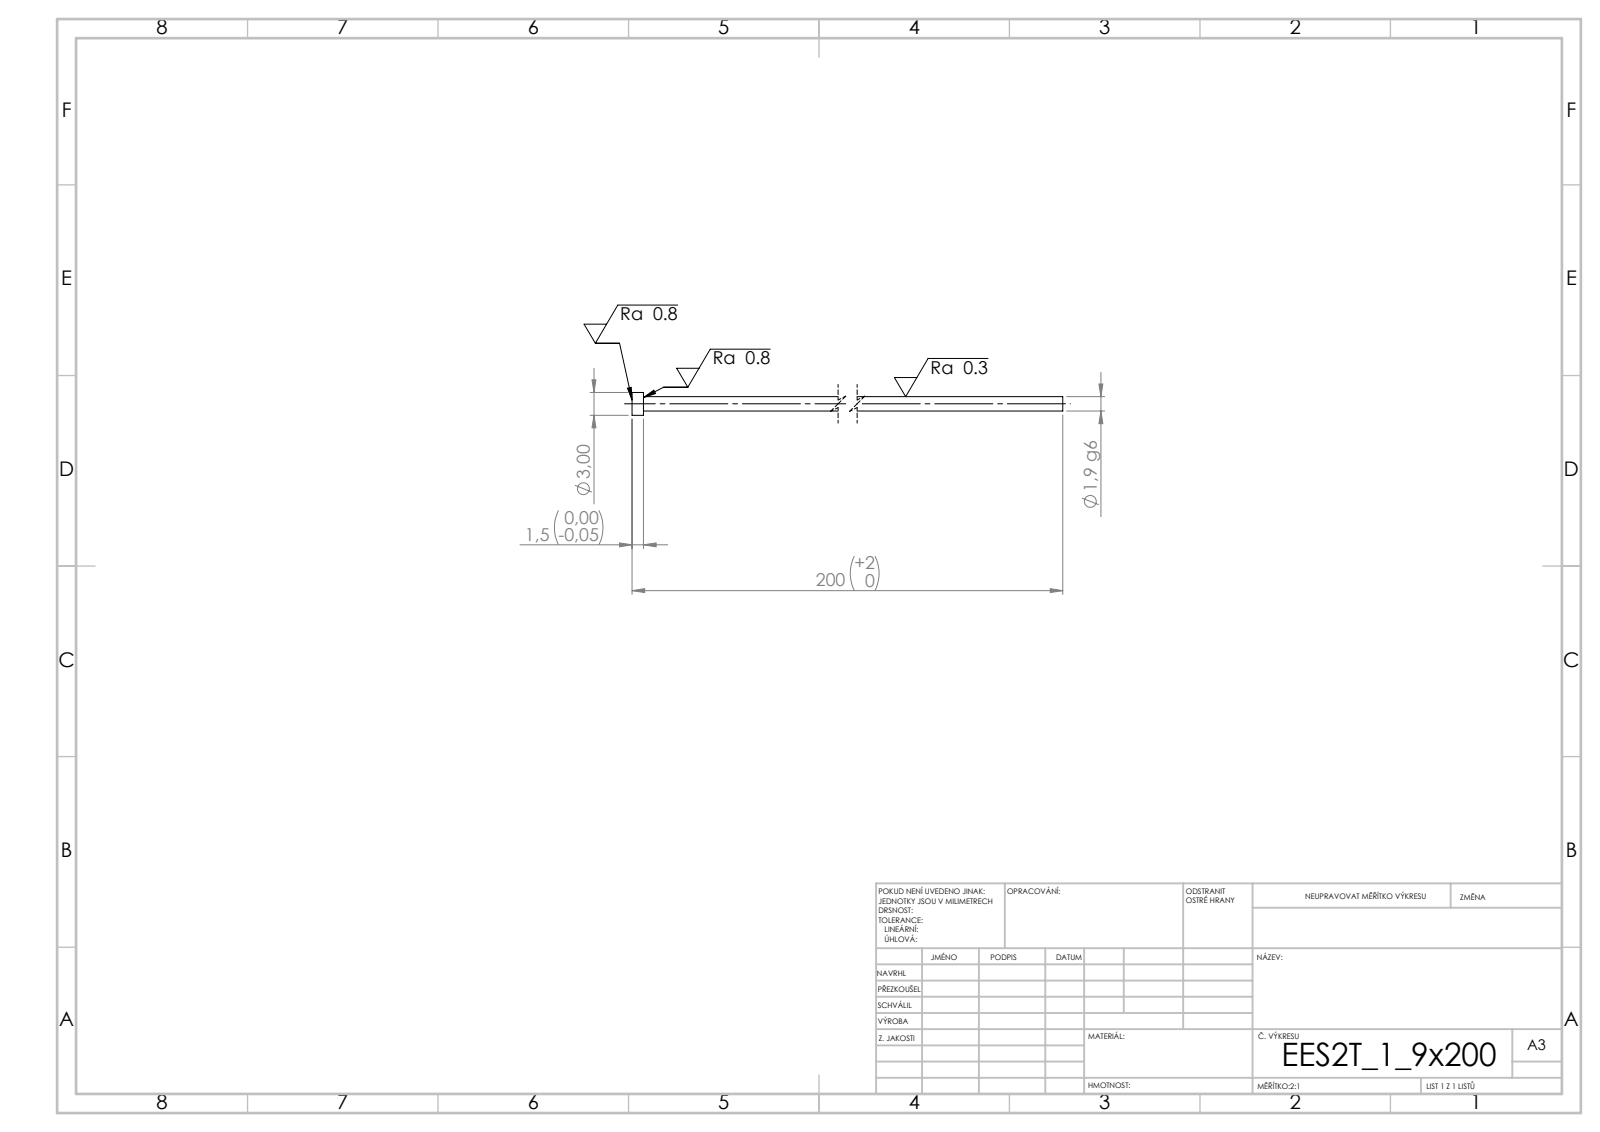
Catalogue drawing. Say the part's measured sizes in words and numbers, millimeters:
Its 3-D file was written by "SolidWorks 2019 (CONFIG_CONTROL_DESIGN)". It is 1 solid with 7 faces: 3 planar, 4 cylindrical and 0 other. Overall it measures 200 by 3 by 3 millimeters. Its volume is 573 cubic millimeters and its surface area 1 213 square millimeters. Round bosses or shafts: 1 of diameter 3, 1 of diameter 1.9. The main face-to-face distances are 1.5, 200, 198.5.
